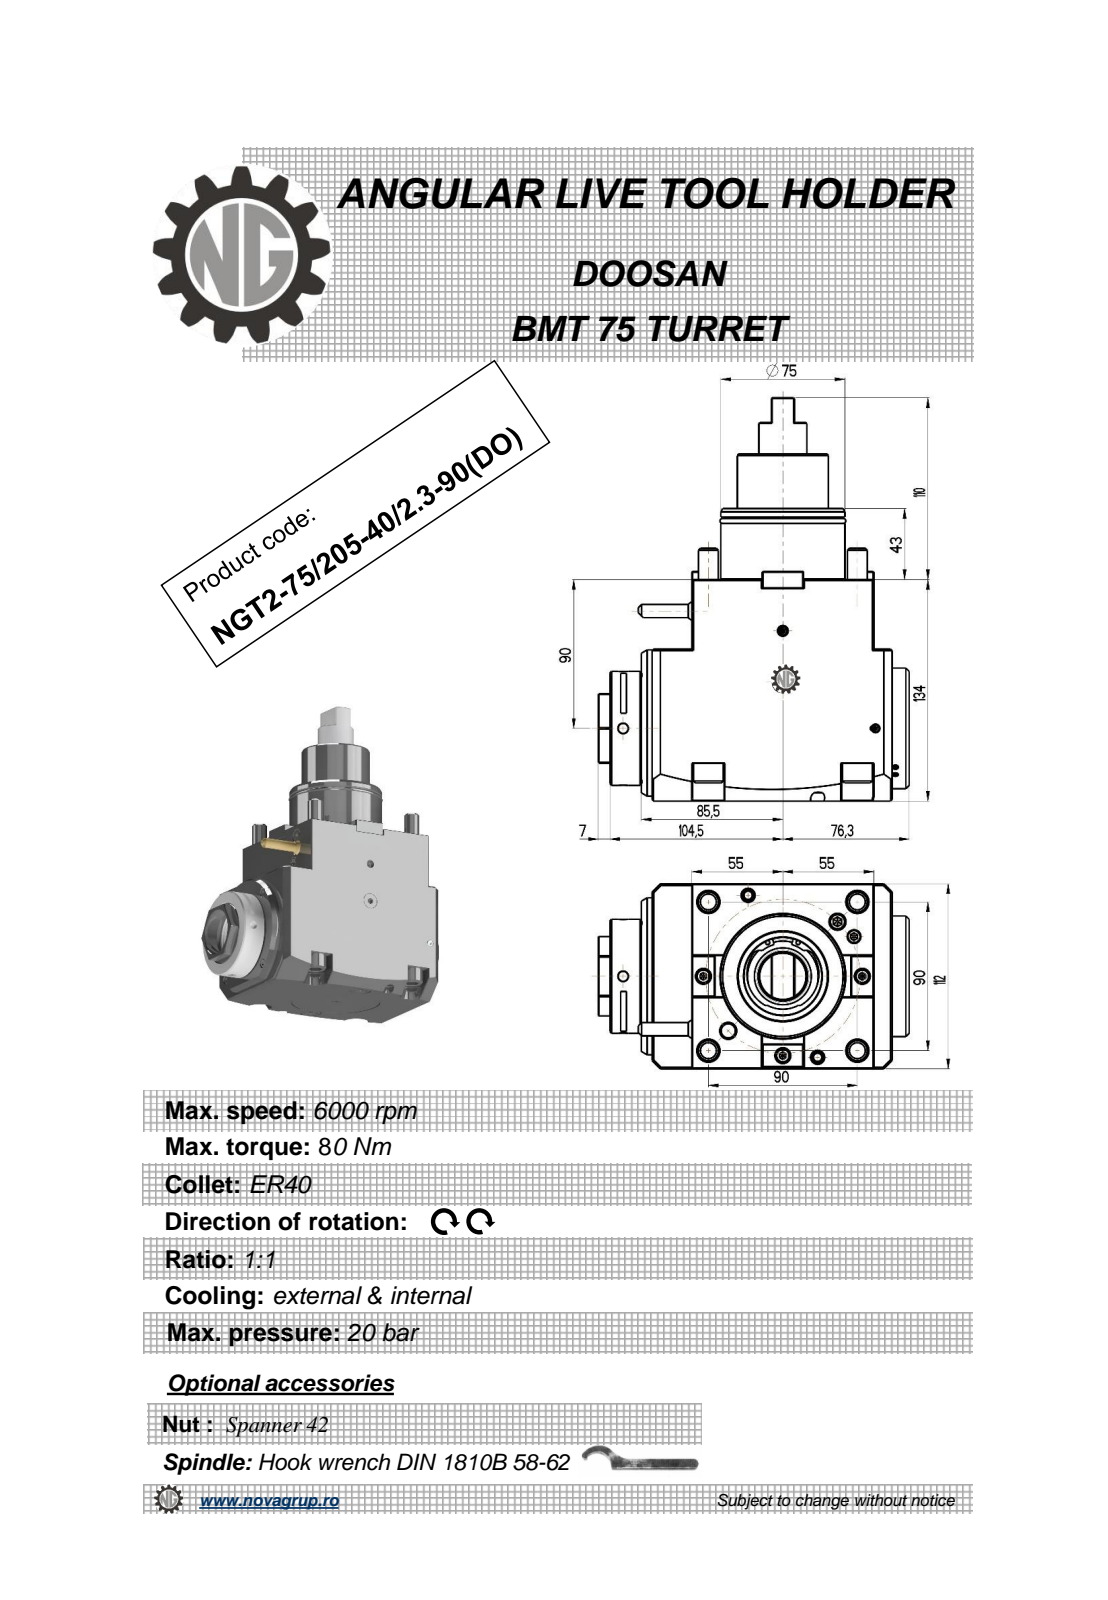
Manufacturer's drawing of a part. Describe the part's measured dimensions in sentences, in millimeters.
The part is named "NGT2_75_205_40_1_3_90_DO". Its 3-D file was written by "PRO/ENGINEER BY PARAMETRIC TECHNOLOGY CORPORATION, 2010280 (CONFIG_CONTROL_DESIGN)". It is 2 solids with 301 faces: 151 planar, 73 cylindrical and 77 other. Overall it measures 244 by 187.8 by 112 millimeters. Its volume is 2 428 000 cubic millimeters and its surface area 140 636 square millimeters. Round holes: 2 of diameter 6, 2 of diameter 8.5, 1 of diameter 3, 1 of diameter 5, 1 of diameter 36.2. Round bosses or shafts: 4 of diameter 18, 4 of diameter 12, 1 of diameter 95, 1 of diameter 75, 1 of diameter 74, 1 of diameter 73, 1 of diameter 70, 1 of diameter 69. Partial cylindrical surfaces (rounded edges, fillets, slot ends): 4 of radius 9.5, 2 of radius 0.8, 2 of radius 350, 1 of radius 24. The main face-to-face distances are 112, 134, 11, 110, 121, 42, 92, 131.3, 21.3, 10.3. The hole center spacings are 71.56, 77.88, 93.34, 133.64.
